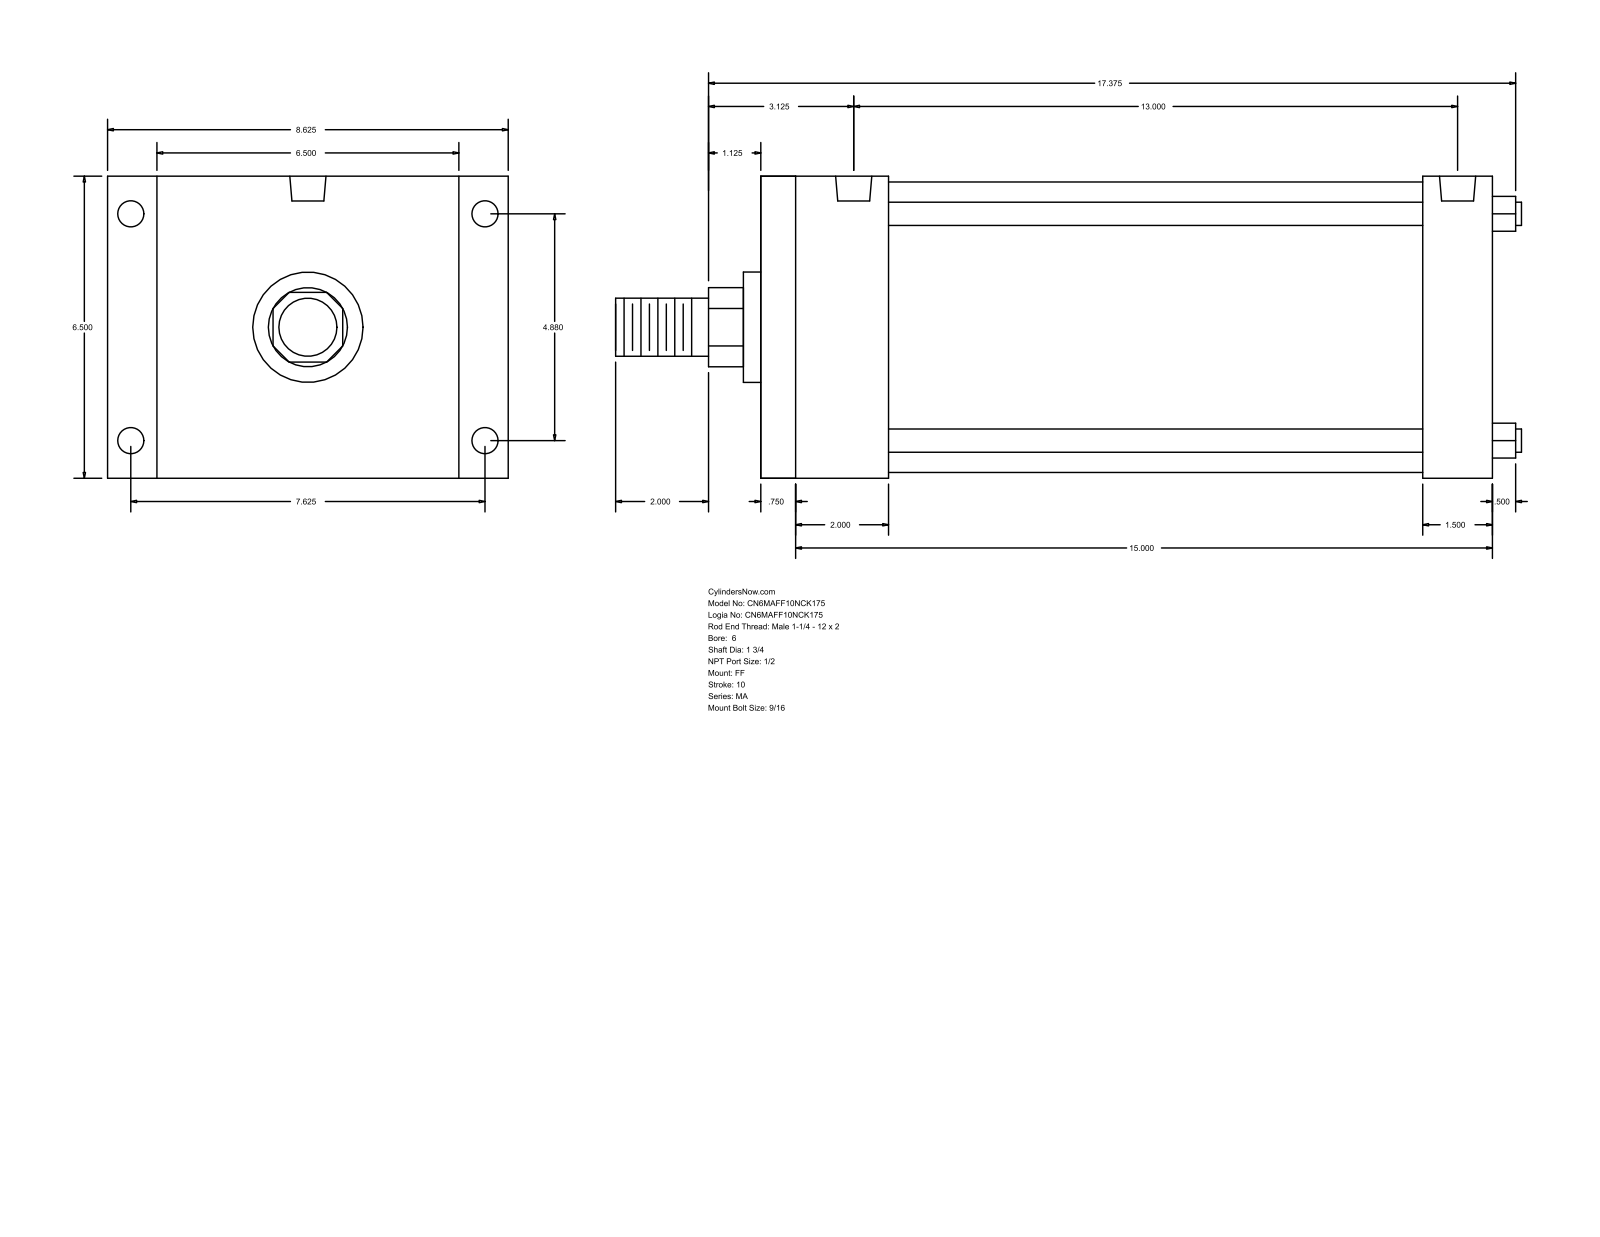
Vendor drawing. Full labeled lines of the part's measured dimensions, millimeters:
Part name (STEP PRODUCT): MA_FF__0600_1.75
STEP written by: GSSL Pune (CONFIG_CONTROL_DESIGN)
Units: millimetres
Bodies: 0 solids, 92 faces (64 planar, 28 cylindrical, 0 other)
Overall size (bounding box): 495.3 × 219.07 × 165.1
Round holes (diameter × count): ⌀14.29 ×4, ⌀17.46 ×4, ⌀19.77 ×2
Round bosses / shafts (diameter × count): ⌀12.7 ×4, ⌀158.75 ×1, ⌀60.33 ×1, ⌀44.45 ×1, ⌀31.75 ×1
Partial cylindrical surfaces — rounded edges, fillets, slot ends (radius × count): R21.63 ×1
Main face-to-face distances: 165.1, 400.05, 19.05, 381, 50.8, 69.85, 342.9, 38.1, 330.2, 361.95
Hole centre spacings: 123.96, 193.68, 229.95, 330.19
